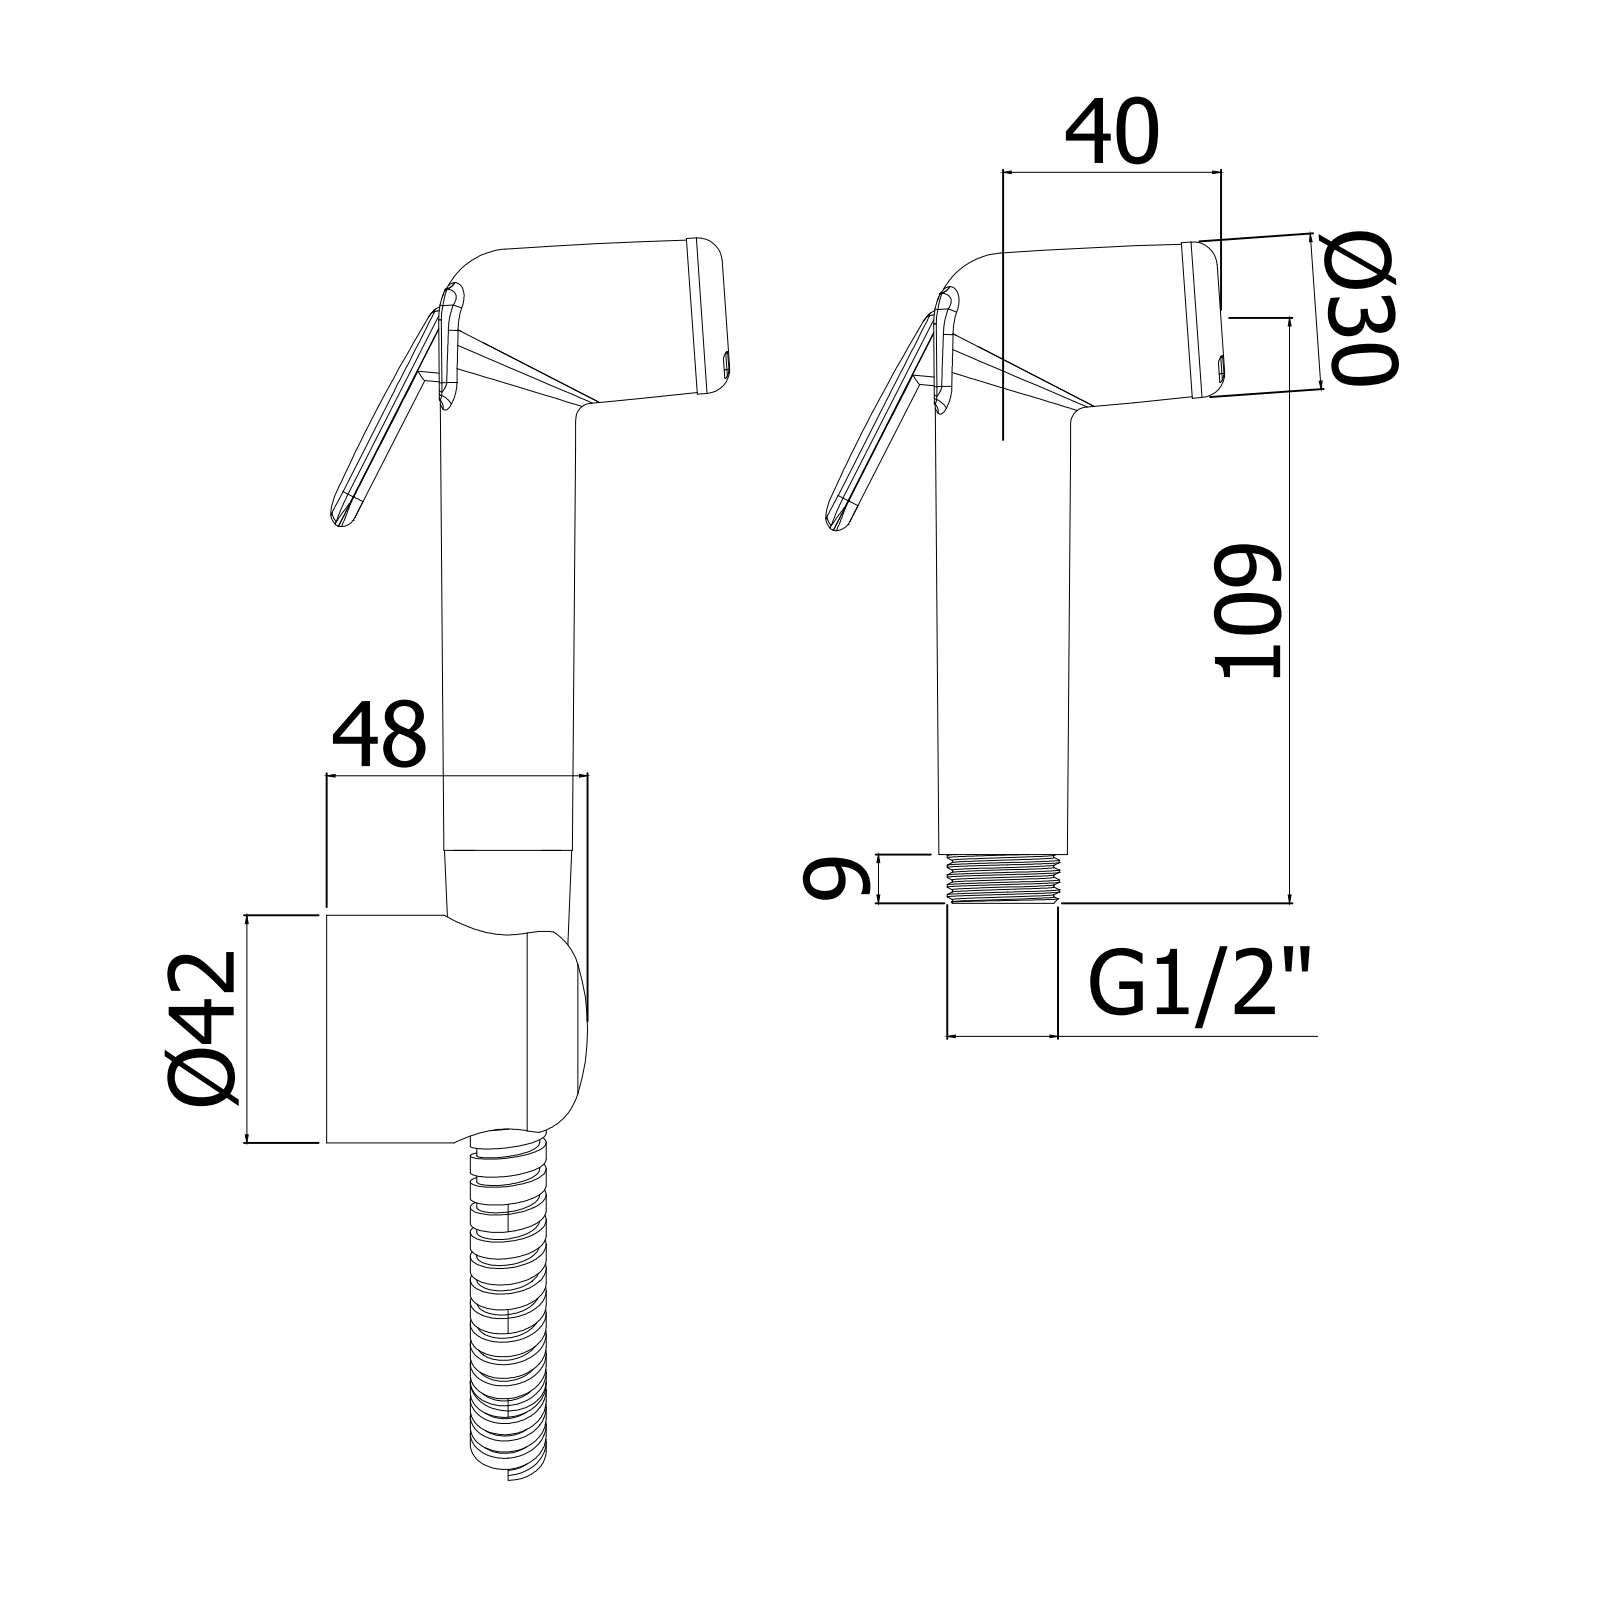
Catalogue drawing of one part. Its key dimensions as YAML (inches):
part_name: "ZDUP099CR"
step_written_by: "CREO PARAMETRIC BY PTC INC, 2020044 (CONFIG_CONTROL_DESIGN)"
units: inches
bodies: {solids: 3, faces: 754, planar: 130, cylindrical: 251, other: 373}
overall_size: [9.032, 2.93, 2.72]
volume: 4.784
surface_area: 86.79
round_holes:
  - {diameter: 0.051, count: 16}
  - {diameter: 0.197, count: 2}
  - {diameter: 0.315, count: 2}
  - {diameter: 0.071, count: 1}
  - {diameter: 0.138, count: 1}
  - {diameter: 0.203, count: 1}
  - {diameter: 0.394, count: 1}
  - {diameter: 0.409, count: 1}
  - {diameter: 0.575, count: 1}
  - {diameter: 0.596, count: 1}
  - {diameter: 0.701, count: 1}
  - {diameter: 0.929, count: 1}
round_bosses_or_shafts:
  - {diameter: 0.472, count: 2}
  - {diameter: 1.654, count: 1}
  - {diameter: 1.134, count: 1}
  - {diameter: 0.913, count: 1}
  - {diameter: 0.843, count: 1}
  - {diameter: 0.823, count: 1}
  - {diameter: 0.661, count: 1}
  - {diameter: 0.567, count: 1}
partial_cylinders:
  - {radius: 0.006, count: 28}
  - {radius: 0.063, count: 6}
  - {radius: 0.118, count: 5}
  - {radius: 0.02, count: 4}
  - {radius: 0.02, count: 4}
  - {radius: 0.035, count: 4}
  - {radius: 0.079, count: 4}
  - {radius: 0.059, count: 3}
face_to_face_distances: [0.079, 0.315, 0.65, 0.078, 0.572, 0.118, 0.728, 0.364, 0.157, 0.65]
hole_center_spacings: [0.246, 0.161, 0.4, 0.342, 0.115, 0.237, 0.298, 0.115]
